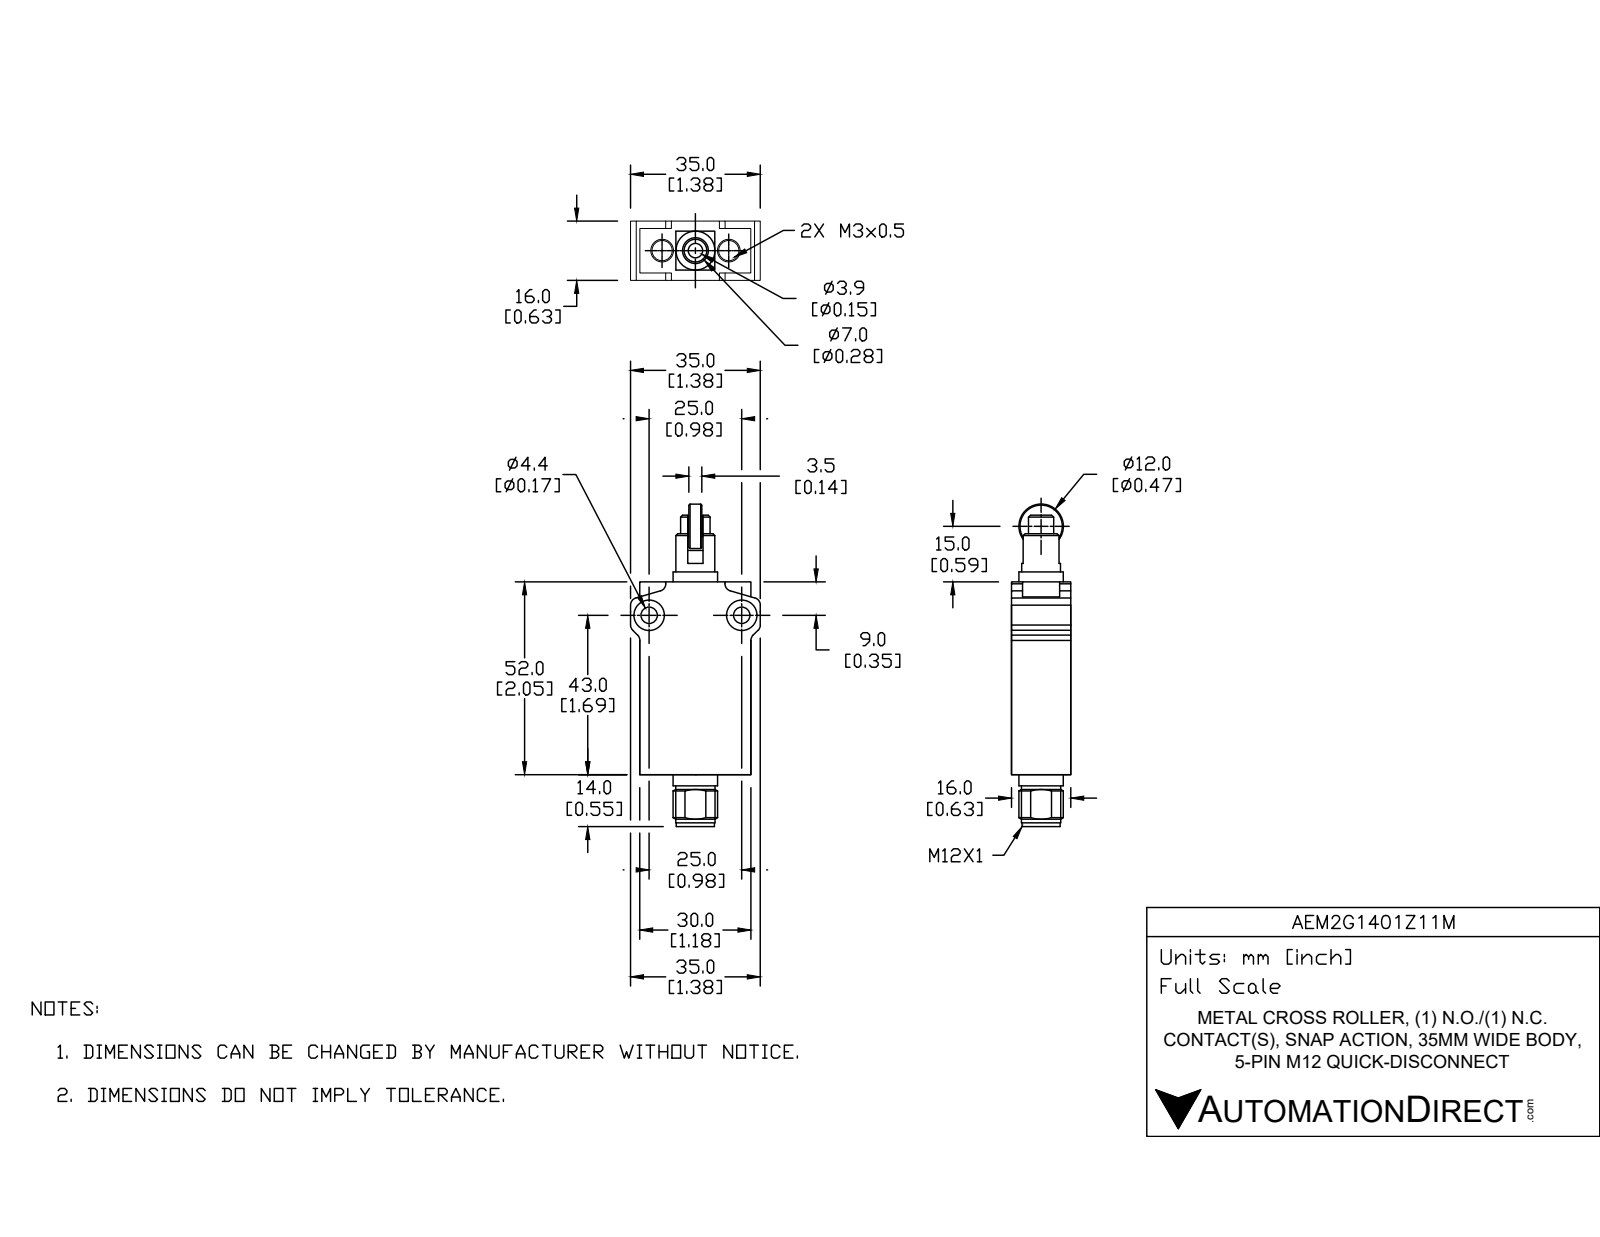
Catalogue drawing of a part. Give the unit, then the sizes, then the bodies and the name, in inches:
Units: inches
Overall size (bounding box): 3.425 × 1.378 × 0.63
Round holes (diameter × count): ⌀0.118 ×2, ⌀0.173 ×2, ⌀0.323 ×2, ⌀0.317 ×1
Round bosses / shafts (diameter × count): ⌀0.472 ×2, ⌀0.417 ×1, ⌀0.413 ×1, ⌀0.406 ×1, ⌀0.313 ×1, ⌀0.22 ×1
Partial cylindrical surfaces — rounded edges, fillets, slot ends (radius × count): R0.079 ×8, R0.256 ×1
Main face-to-face distances: 0.63, 1.181, 2.047, 0.472, 1.858, 0.189, 0.15, 0.157, 0.51, 0.671
Hole centre spacings: 0.374, 0.748, 0.984
Volume: 1.643 in³ · Surface area: 14.59 in²
Bodies: 4 solids, 180 faces (67 planar, 72 cylindrical, 41 other)
Part name (STEP PRODUCT): AEM2G1401Z11M
STEP written by: SolidWorks 2017 (AUTOMOTIVE_DESIGN)
